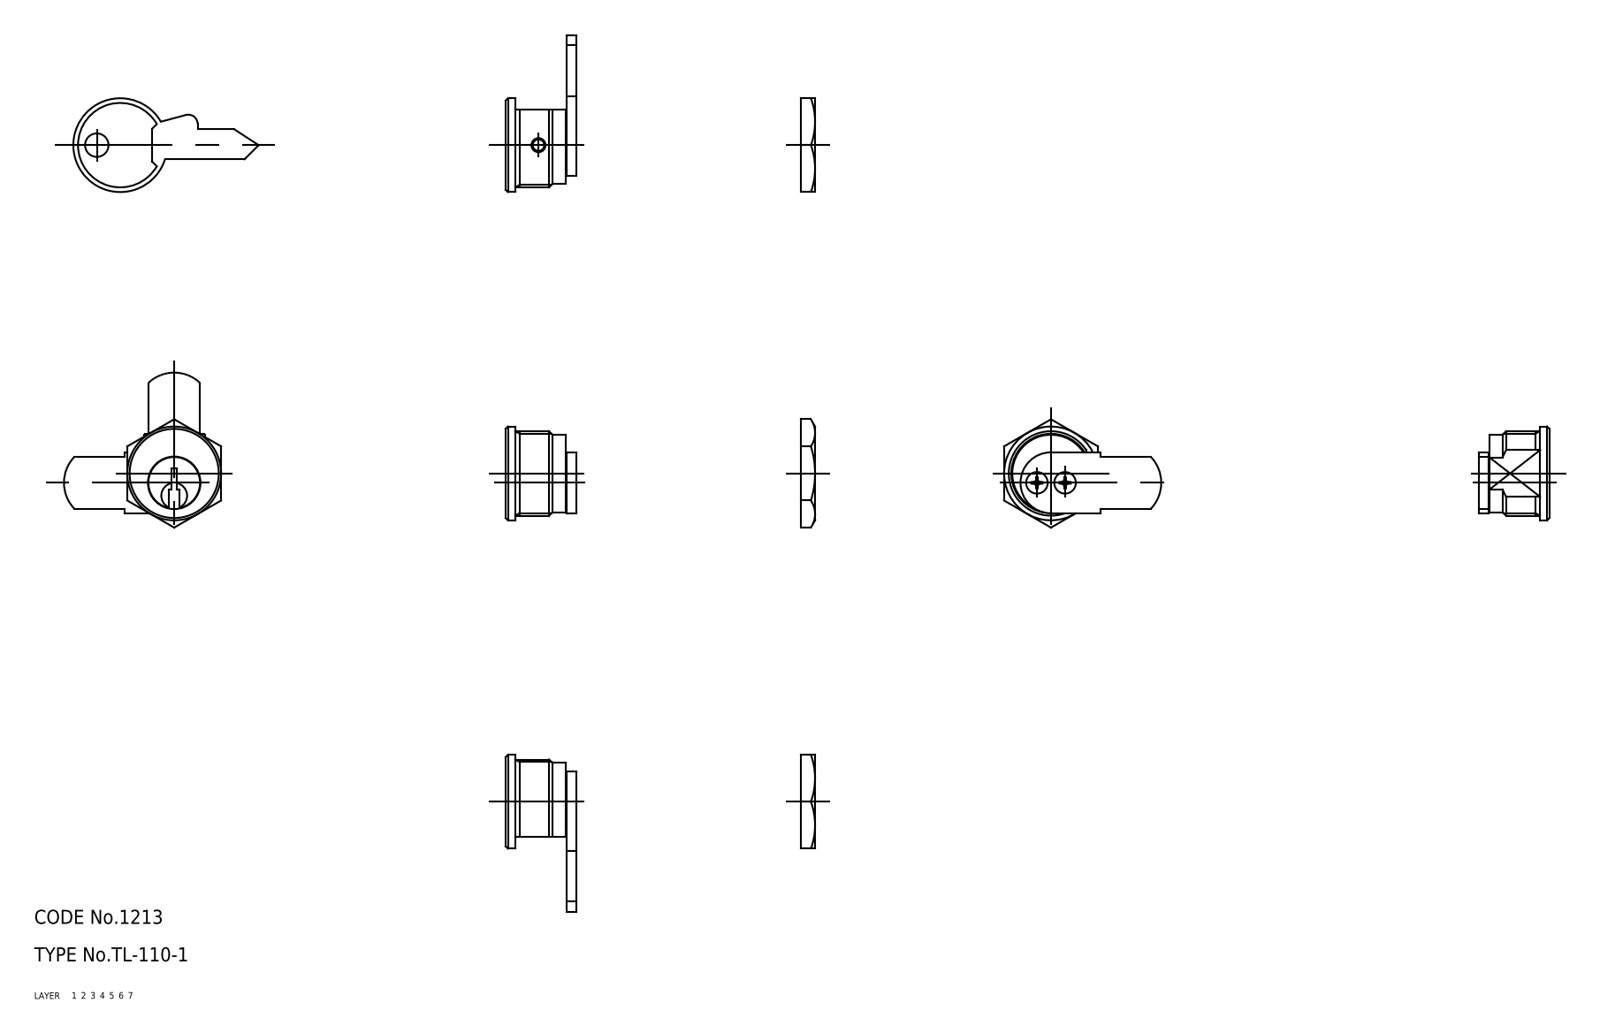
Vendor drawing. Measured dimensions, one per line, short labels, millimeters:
name: screw; nut; lock; key (+2 more)
written by: CADfix (AUTOMOTIVE_DESIGN)
unit: mm
bodies: 6 solids, 127 faces (0 planar, 0 cylindrical, 127 other)
size: 81.55 × 33.5 × 25.55
volume: 4 627 mm³; area: 4 278 mm²
